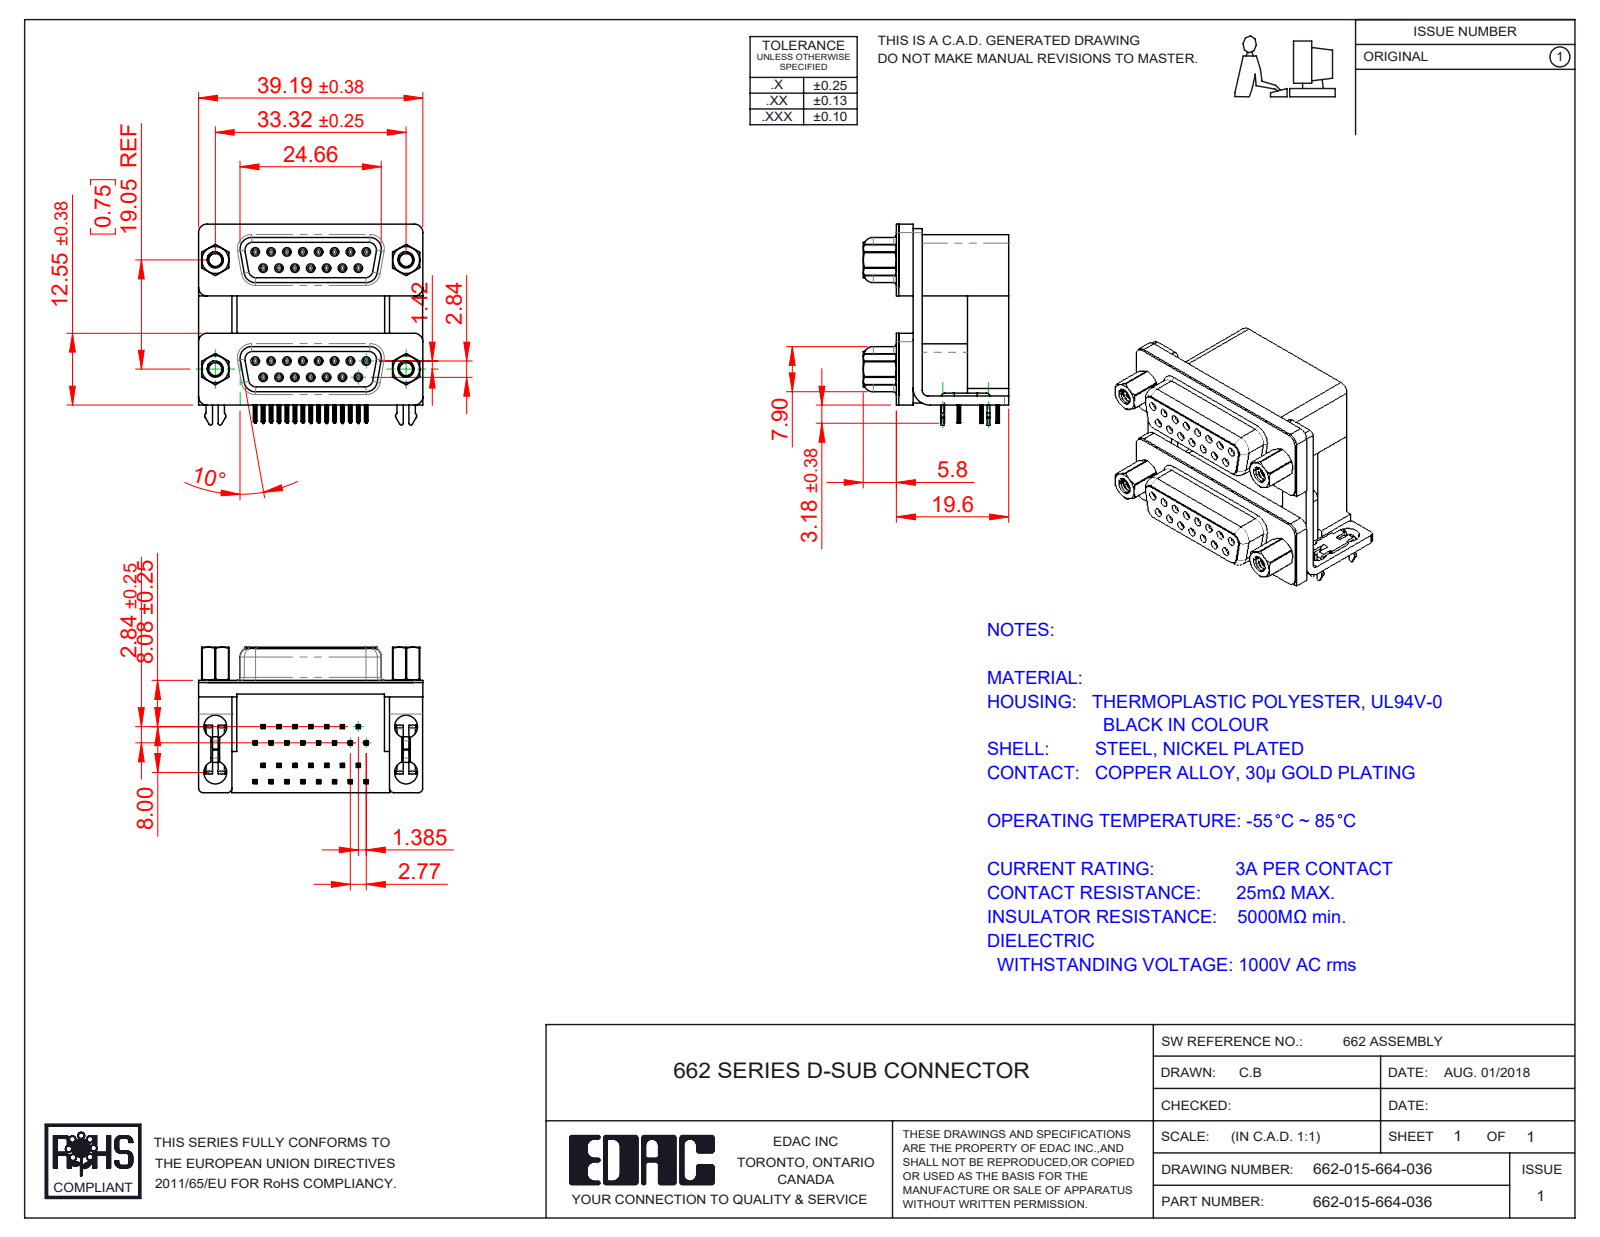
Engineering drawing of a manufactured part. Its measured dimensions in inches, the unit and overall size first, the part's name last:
Units: inches
Overall size (bounding box): 1.543 × 1.382 × 1
Round holes (diameter × count): ⌀0.031 ×30, ⌀0.035 ×30, ⌀0.157 ×8, ⌀0.089 ×4, ⌀0.09 ×4, ⌀0.138 ×4, ⌀0.189 ×4, ⌀0.197 ×4
Round bosses / shafts (diameter × count): ⌀0.047 ×30, ⌀0.193 ×4, ⌀0.187 ×4, ⌀0.154 ×4, ⌀0.11 ×4
Partial cylindrical surfaces — rounded edges, fillets, slot ends (radius × count): R0.004 ×242, R0.006 ×120, R0.014 ×60, R0.013 ×30, R0.053 ×16, R0.059 ×16, R0.011 ×14, R0.02 ×12
Main face-to-face distances: 0.016, 0.75, 0.756, 0.472, 0.098, 0.657, 0.114, 0.283, 0.374, 0.488
Hole centre spacings: 0.124, 0.758, 0.109, 0.781, 0.218, 0.327, 0.75, 0.818
Volume: 1.004 in³ · Surface area: 29.68 in²
Bodies: 47 solids, 5266 faces (2342 planar, 1368 cylindrical, 1556 other)
Part name (STEP PRODUCT): 662 Contact Bottom Lower; 662 2 Prong Board Lock_3; 662 Housing Upper_15 Contacts M; 662 4-40 Hex Standoff 5 (+8 more)
STEP written by: SolidWorks 2020 (CONFIG_CONTROL_DESIGN)
